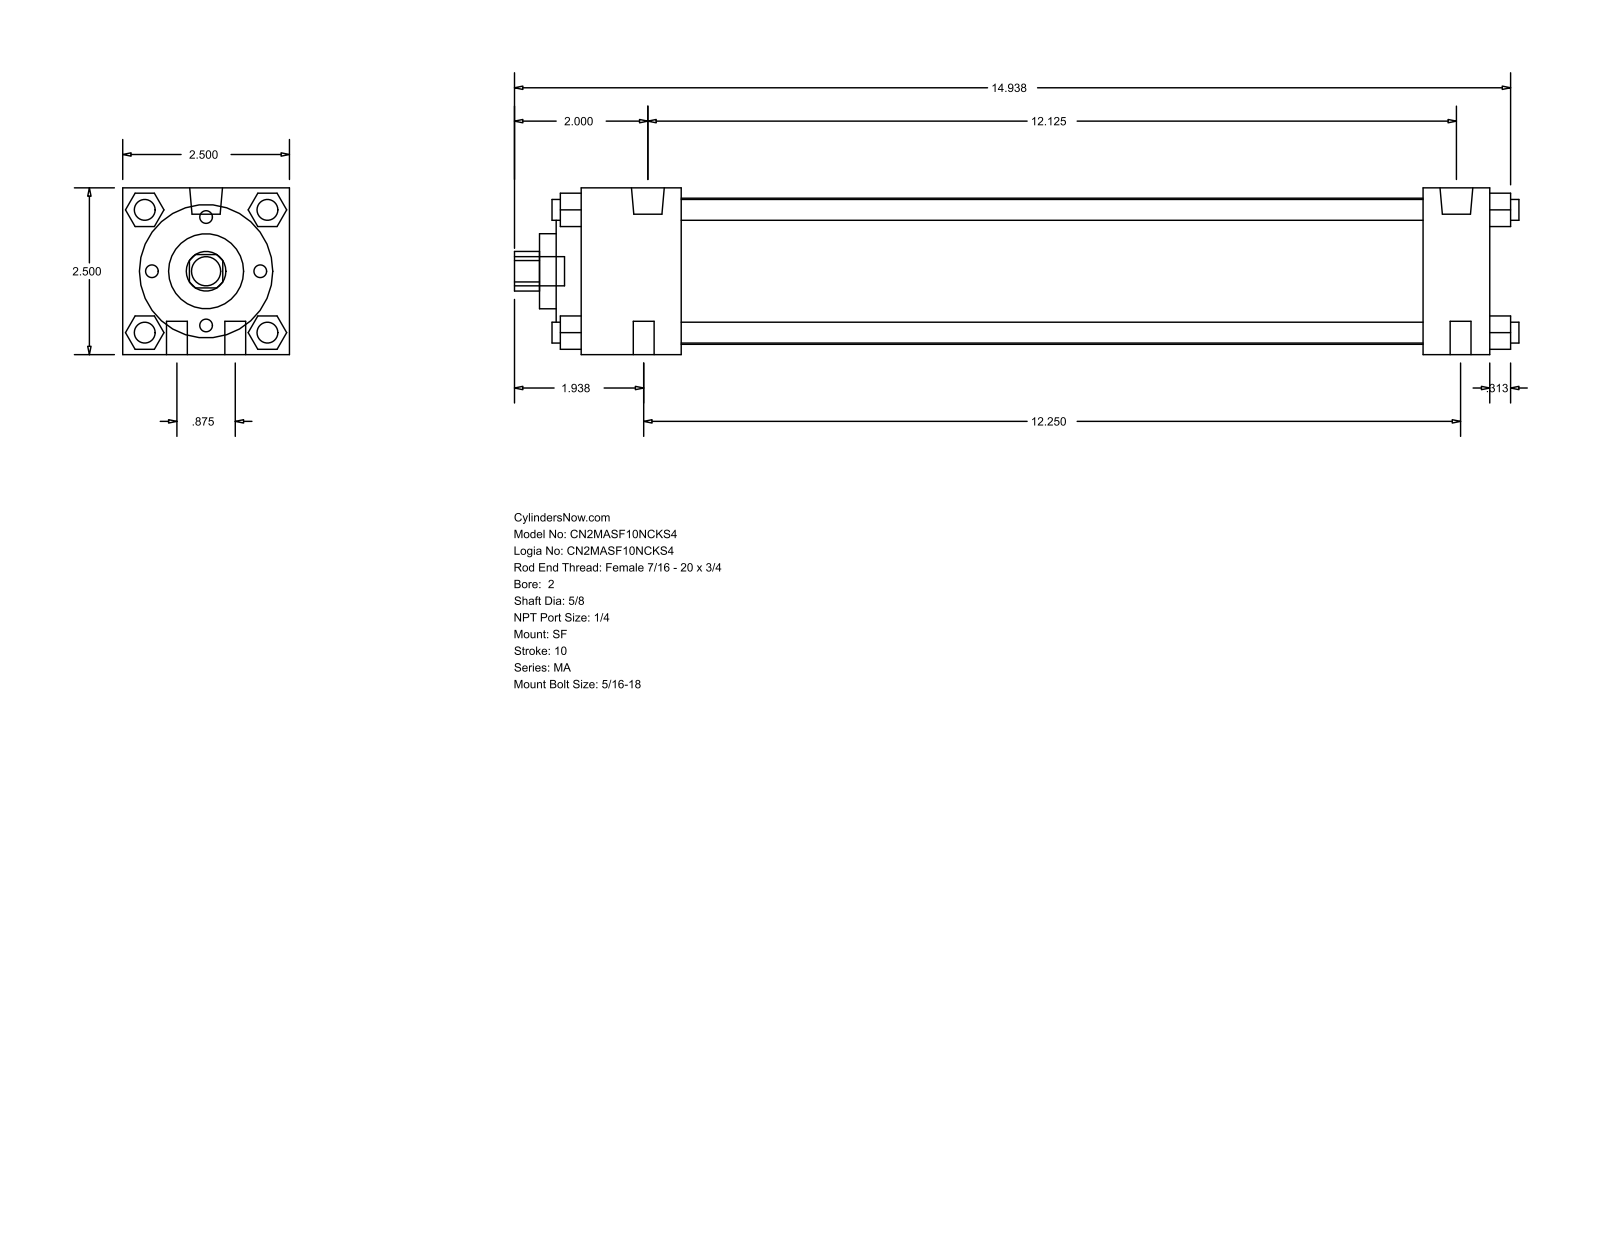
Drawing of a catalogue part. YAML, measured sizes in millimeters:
part_name: "MA_SF__0200_0.625"
step_written_by: "GSSL Pune (CONFIG_CONTROL_DESIGN)"
units: millimeters
bodies: {solids: 0, faces: 126, planar: 95, cylindrical: 31, other: 0}
overall_size: [382.59, 63.5, 63.5]
round_holes:
  - {diameter: 15.88, count: 1}
  - {diameter: 28.57, count: 1}
  - {diameter: 50.8, count: 1}
  - {diameter: 55.63, count: 1}
round_bosses_or_shafts:
  - {diameter: 7.94, count: 10}
  - {diameter: 12.49, count: 2}
  - {diameter: 11.11, count: 1}
partial_cylinders:
  - {radius: 7.54, count: 1}
face_to_face_distances: [63.5, 12.7, 38.1, 9.52, 346.08, 320.67, 25.41, 282.57, 307.98, 47.62]
